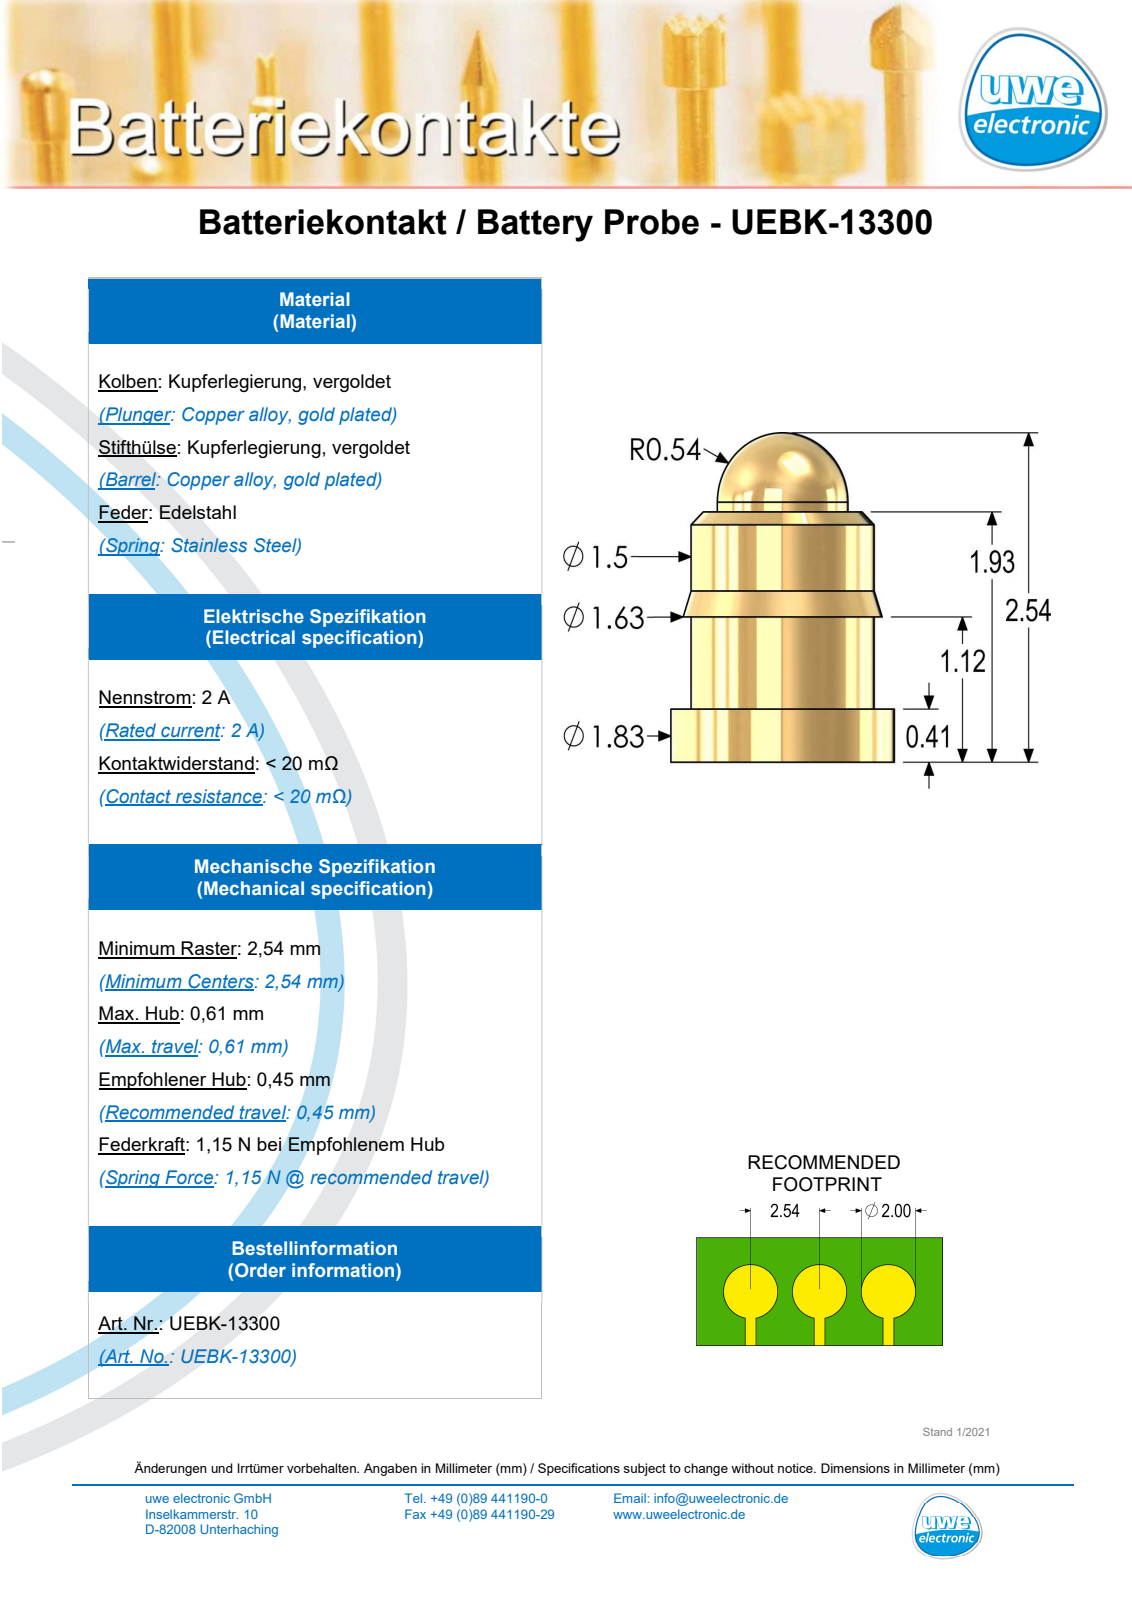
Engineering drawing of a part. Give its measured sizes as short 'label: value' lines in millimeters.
name: UEBK-13300
written by: SolidWorks 2019 (AUTOMOTIVE_DESIGN)
unit: mm
bodies: 1 solid, 18 faces (4 planar, 8 cylindrical, 6 other)
size: 2.54 × 1.83 × 1.83
volume: 4 mm³; area: 16 mm²
bosses: 1× ⌀1.83, 1× ⌀1.5, 1× ⌀1.07
face distances: 0.41, 1.93, 1.52, 1.12, 0.71, 0.81
